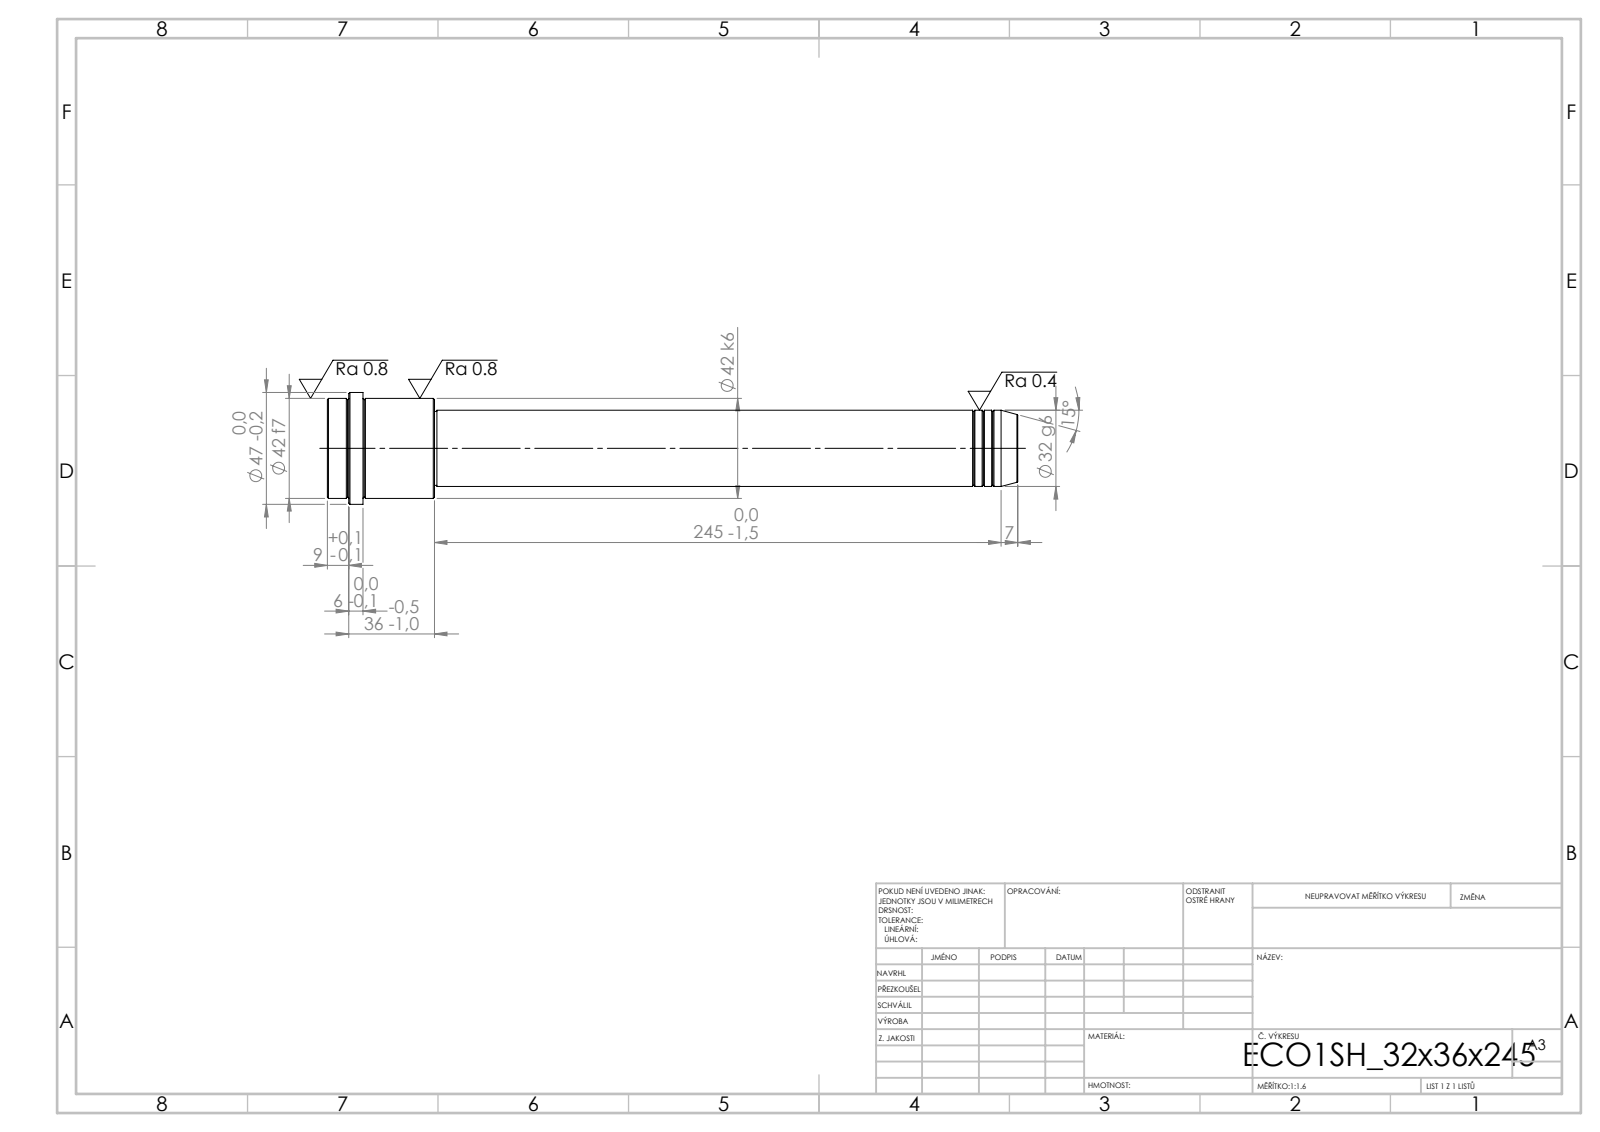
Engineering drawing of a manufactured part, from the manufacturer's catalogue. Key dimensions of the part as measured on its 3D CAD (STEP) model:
STEP written by: SolidWorks 2019 (CONFIG_CONTROL_DESIGN)
Units: millimetres
Bodies: 1 solid, 52 faces (6 planar, 16 cylindrical, 30 other)
Overall size (bounding box): 290 × 47 × 47
Volume: 260 526 mm³ · Surface area: 34 208 mm²
Round bosses / shafts (diameter × count): ⌀47 ×1, ⌀42 ×1, ⌀32 ×1, ⌀31 ×1
Main face-to-face distances: 290, 245, 45, 275, 30, 15, 281, 36, 6, 9
